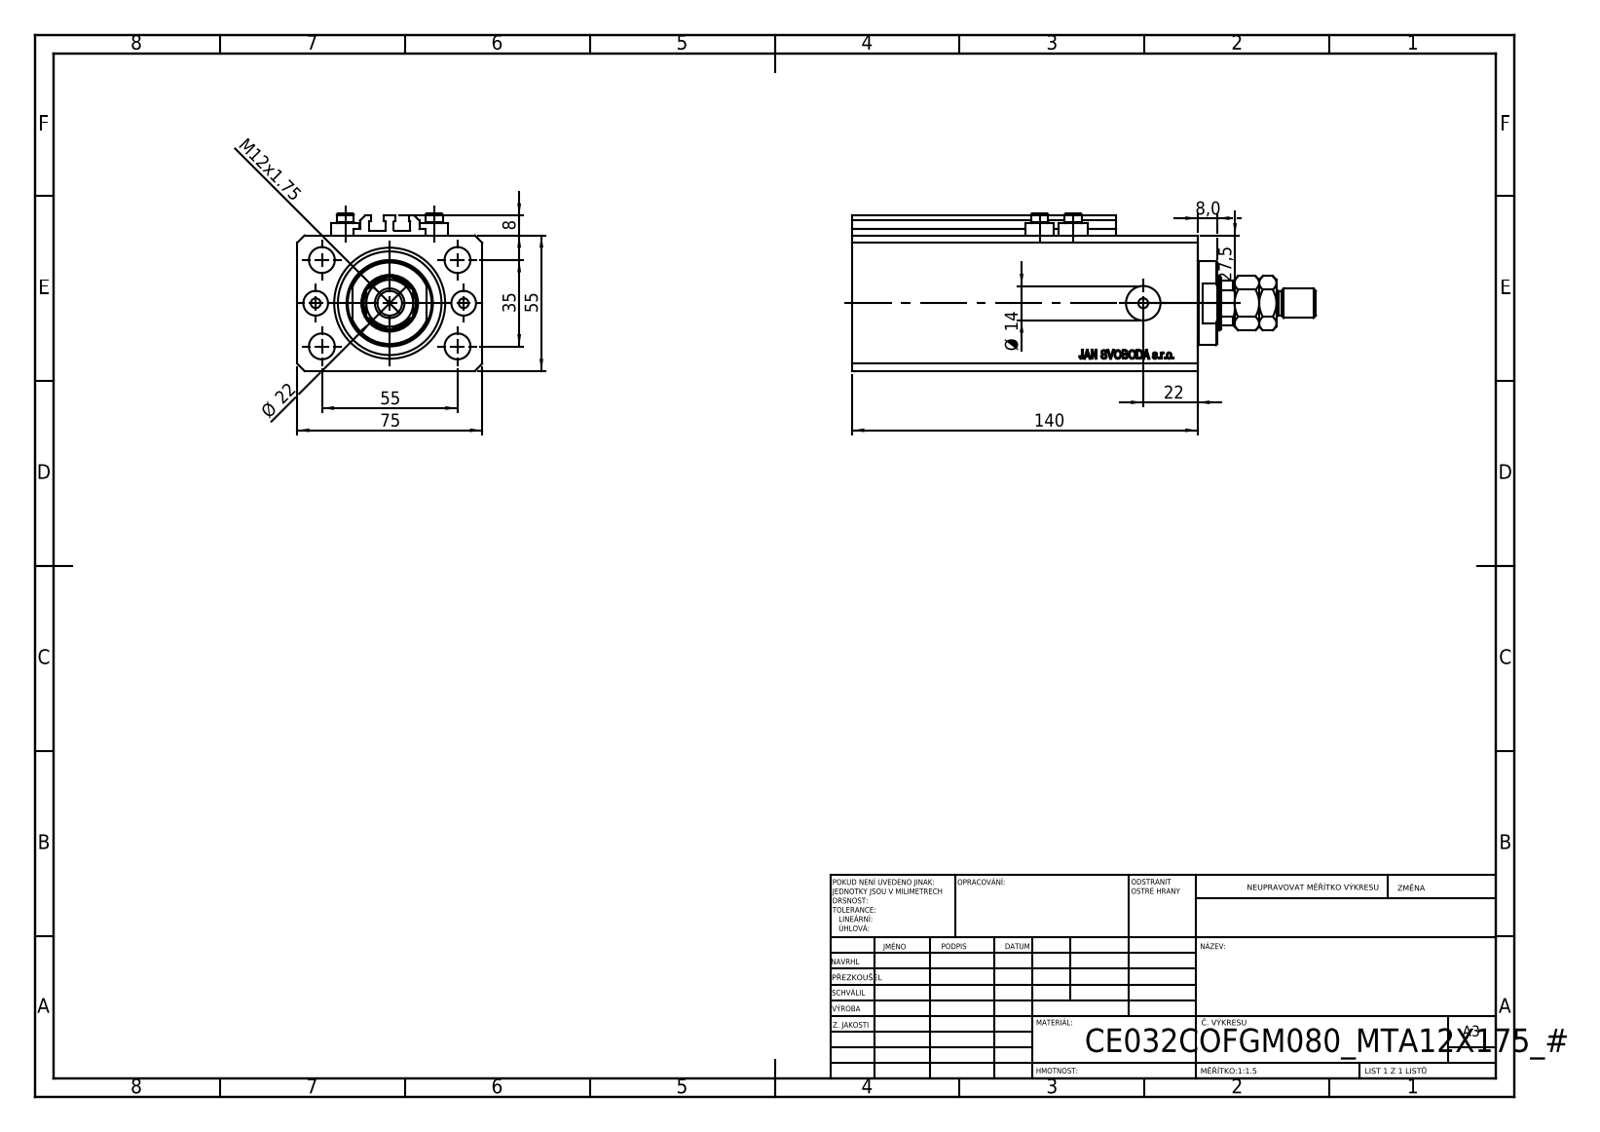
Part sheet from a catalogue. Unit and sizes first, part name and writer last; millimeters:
Units: millimetres
Overall size (bounding box): 188 × 75 × 64
Round holes (diameter × count): ⌀4 ×8, ⌀10.5 ×5, ⌀10 ×2, ⌀14 ×2, ⌀22 ×1, ⌀32 ×1, ⌀45 ×1
Round bosses / shafts (diameter × count): ⌀11.6 ×4, ⌀7 ×4, ⌀34 ×1, ⌀12 ×1, ⌀10 ×1
Partial cylindrical surfaces — rounded edges, fillets, slot ends (radius × count): R0.2 ×10, R10.5 ×1
Main face-to-face distances: 55, 75, 15, 140, 125, 2.5, 9.9, 115.1, 130.1, 2
Hole centre spacings: 17.68, 32.6, 60.1, 13.6, 30, 35, 36, 38.48
Volume: 110 674 mm³ · Surface area: 113 229 mm²
Bodies: 8 solids, 1083 faces (519 planar, 90 cylindrical, 474 other)
Part name (STEP PRODUCT): V250CE_C_Body; V250CE_C_VCP; MTA; V250CE_VC_C (+1 more)
STEP written by: SolidWorks 2019 (CONFIG_CONTROL_DESIGN)
